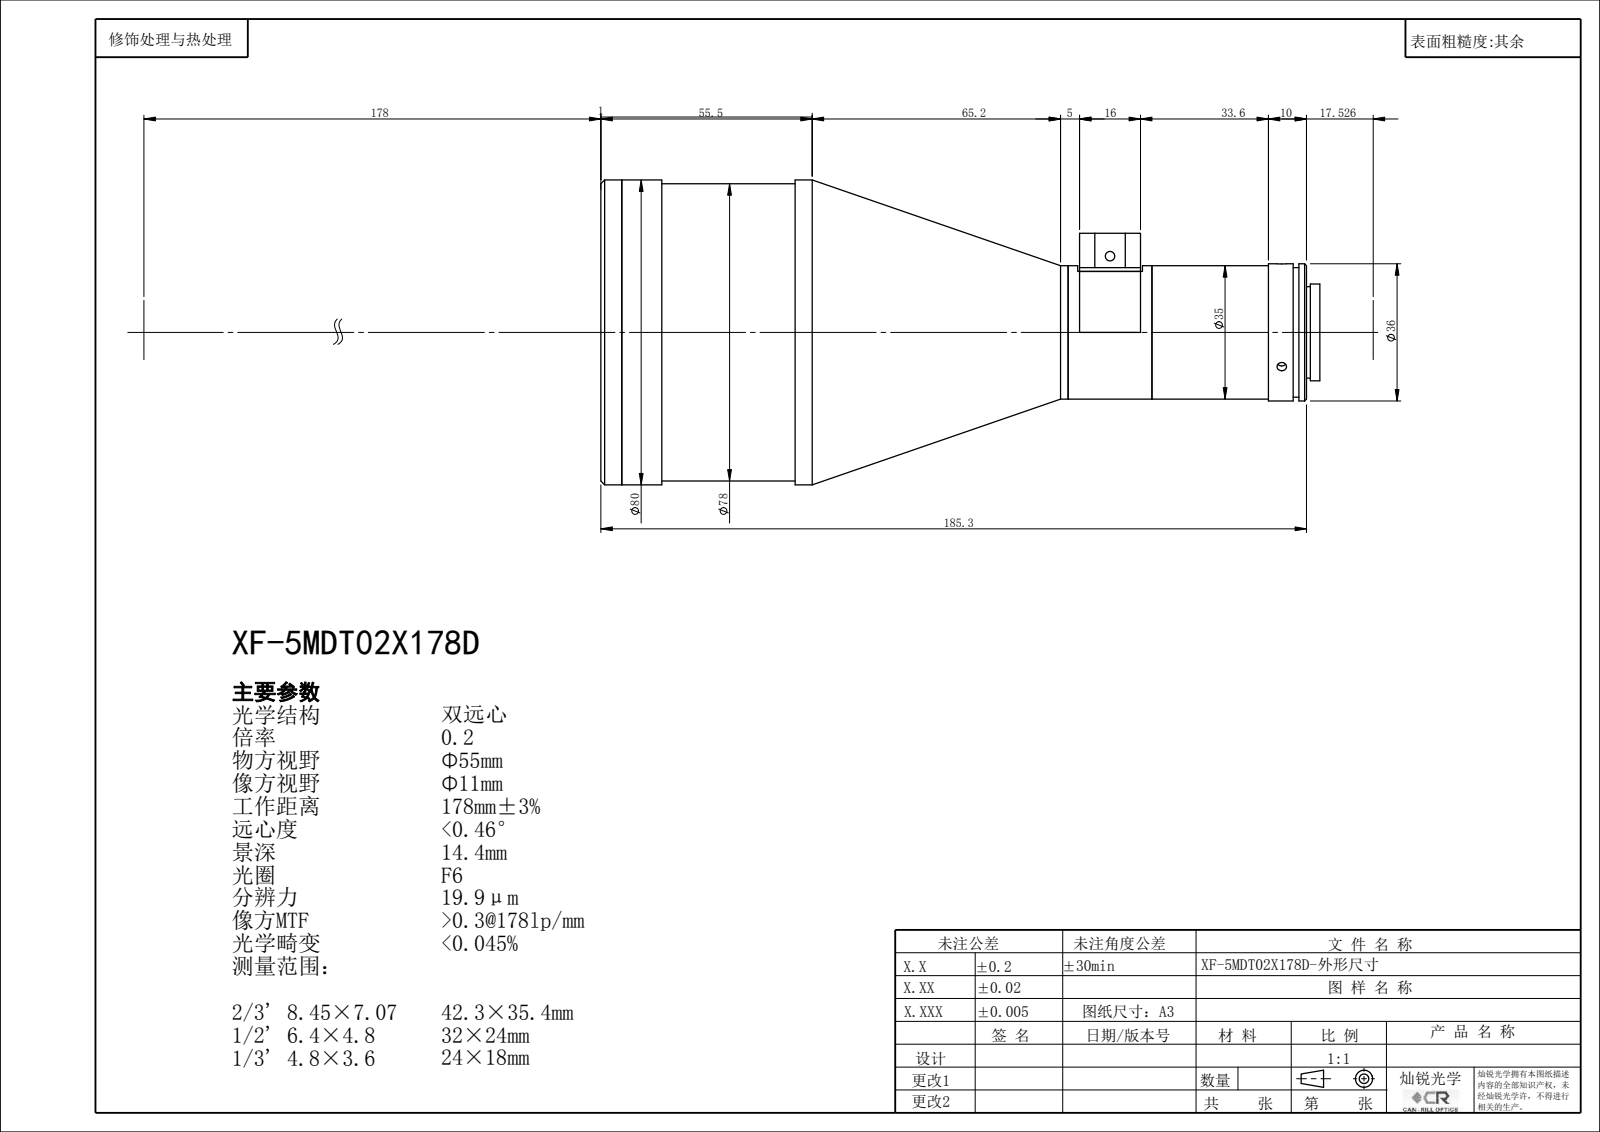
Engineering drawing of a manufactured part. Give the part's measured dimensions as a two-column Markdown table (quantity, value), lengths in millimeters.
| quantity | value |
| --- | --- |
| part name | XF-5MDT02X178D |
| STEP written by | SolidWorks 2014 (CONFIG_CONTROL_DESIGN) |
| units | millimeters |
| bodies | 0 solids, 130 faces (47 planar, 71 cylindrical, 12 other) |
| overall size | 188.8 × 80 × 80 |
| round holes (diameter × count) | 2.5 × 8, 1.6 × 4, 14 × 1, 20 × 1, 21.4 × 1, 25 × 1, 70 × 1, 73 × 1, 76 × 1 |
| round bosses / shafts (diameter × count) | 80 × 1, 78 × 1, 36 × 1, 35 × 1, 34 × 1, 25.4 × 1, 24 × 1 |
| partial cylindrical surfaces (radius × count) | 4 × 4 |
| main face-to-face distances | 5.5, 3, 19, 16, 125.71, 35, 139.21, 144.71, 40.59, 179.8 |
| hole center spacings | 15.98, 11, 30, 31.95, 42.34, 52.77, 45.09 |
